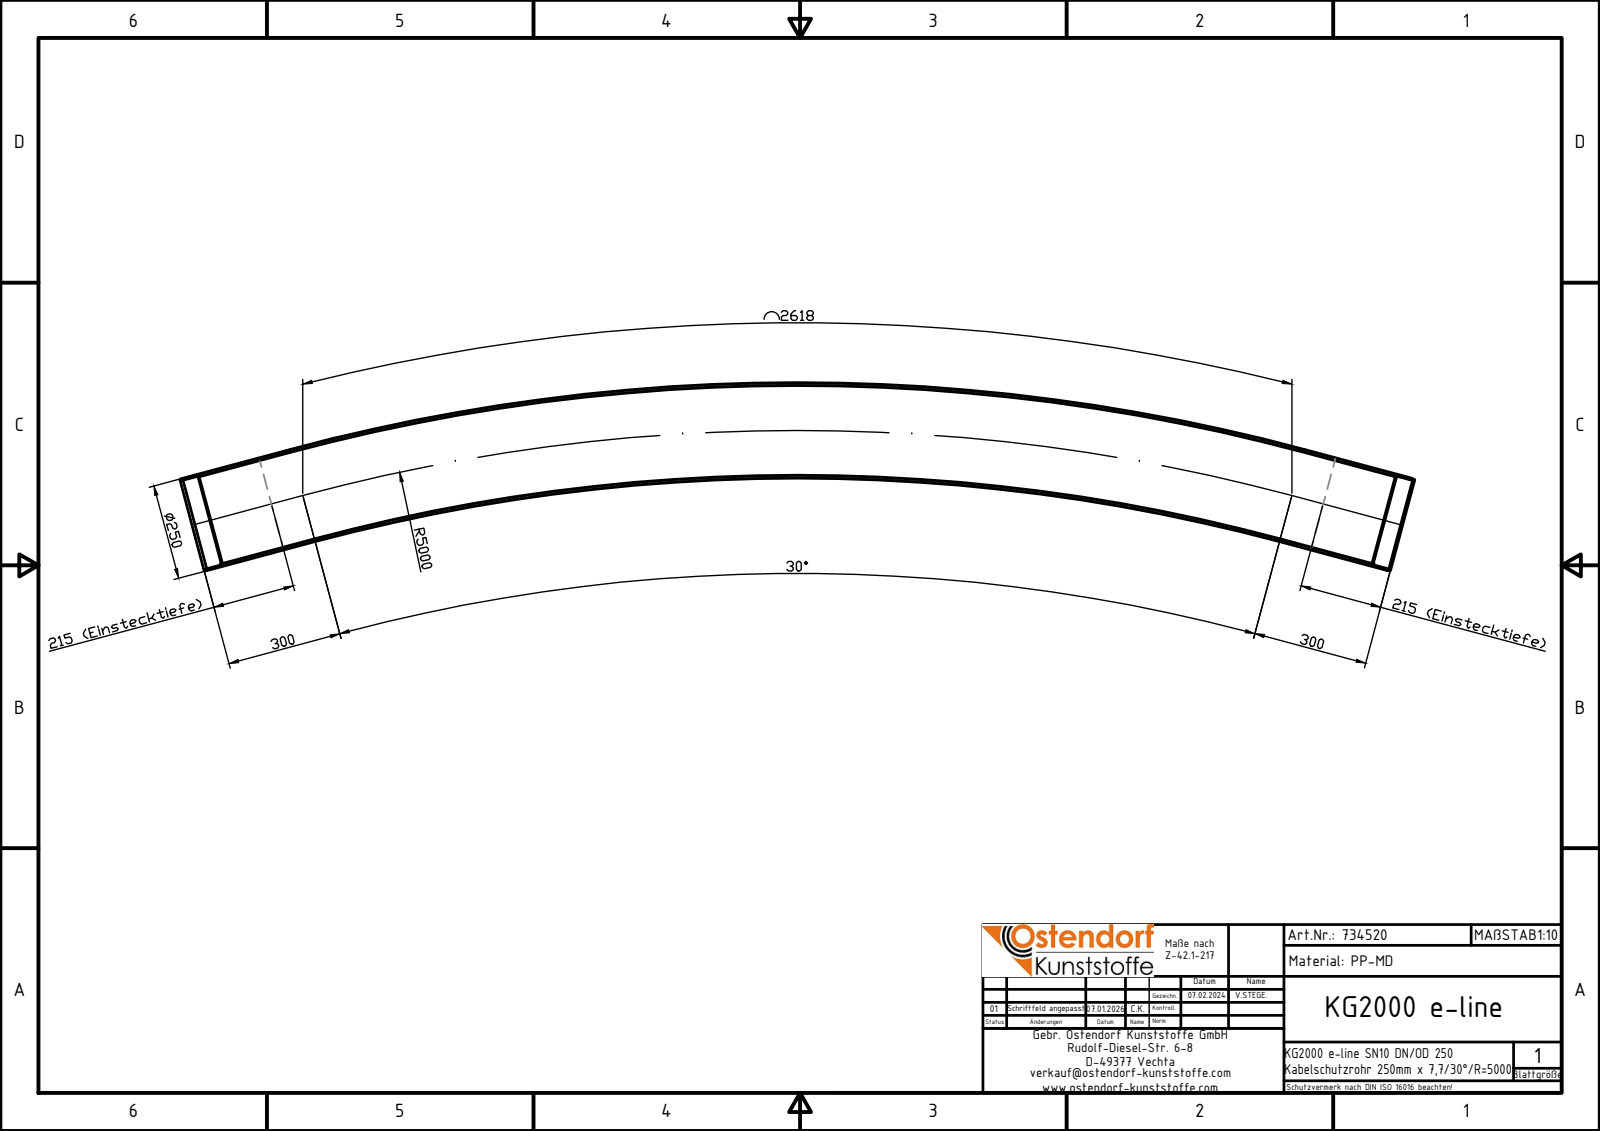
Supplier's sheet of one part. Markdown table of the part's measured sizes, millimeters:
| quantity | value |
| --- | --- |
| part name | 734520z |
| STEP written by | Autodesk Inventor 2024 (AUTOMOTIVE_DESIGN) |
| units | millimeters |
| bodies | 1 solid, 20 faces (2 planar, 6 cylindrical, 12 other) |
| overall size | 323.15 × 49.25 × 25 |
| volume | 18 667 mm³ |
| surface area | 49 048 mm² |
| round holes (diameter × count) | 23.46 × 2, 23.96 × 2 |
| round bosses / shafts (diameter × count) | 25 × 2 |
